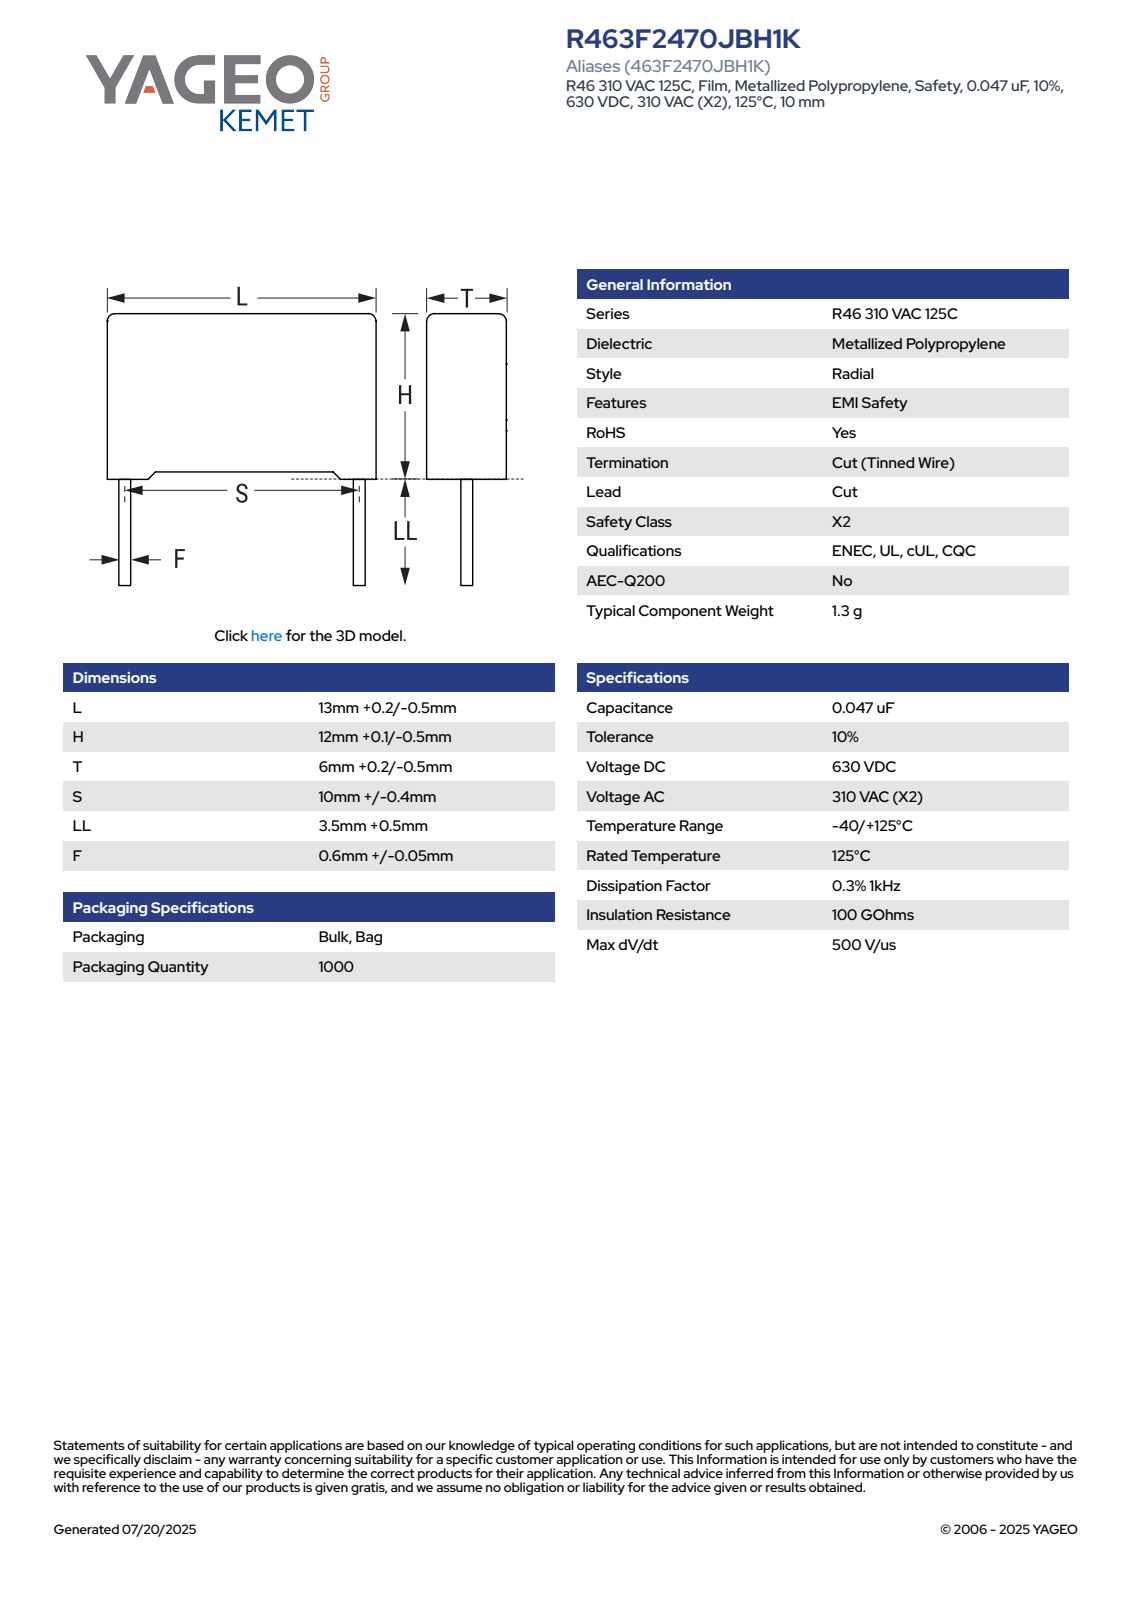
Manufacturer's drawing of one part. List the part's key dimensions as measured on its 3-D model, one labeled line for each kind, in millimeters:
Part name (STEP PRODUCT): CFR_RB2_13X12X6_L13.2H12.1T6.2S10LL4F0.65
STEP written by: SolidWorks 2021 (AUTOMOTIVE_DESIGN)
Units: millimetres
Bodies: 4 solids, 85 faces (77 planar, 8 cylindrical, 0 other)
Overall size (bounding box): 16.1 × 13.2 × 6.21
Volume: 940 mm³ · Surface area: 673 mm²
Round bosses / shafts (diameter × count): ⌀0.65 ×2
Partial cylindrical surfaces — rounded edges, fillets, slot ends (radius × count): R0.5 ×4
Main face-to-face distances: 6.2, 13.2, 11.35, 0.44, 5.76, 0.75, 12.1, 12.76, 5.32, 0.42
